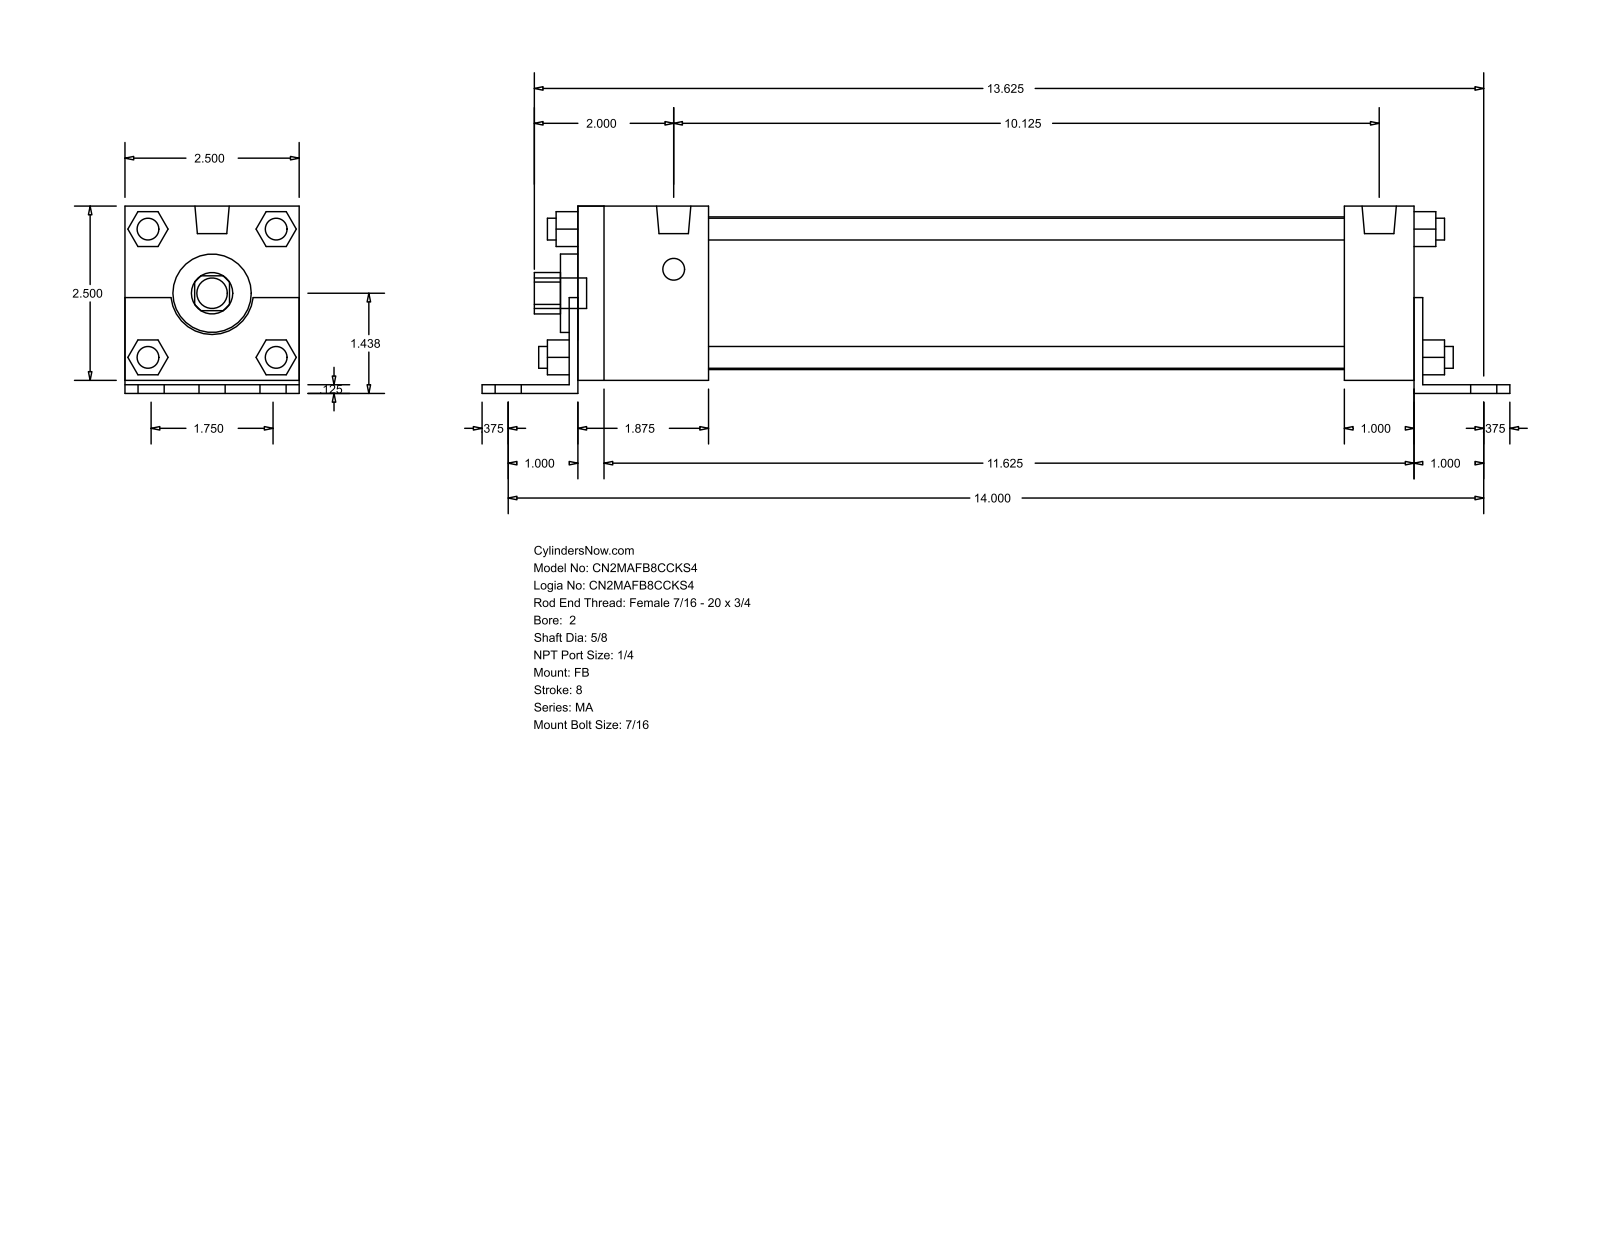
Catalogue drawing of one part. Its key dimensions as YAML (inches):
part_name: "MA_FB__0200_0.625"
step_written_by: "GSSL Pune (CONFIG_CONTROL_DESIGN)"
units: inches
bodies: {solids: 0, faces: 140, planar: 105, cylindrical: 35, other: 0}
overall_size: [14.75, 2.687, 2.5]
round_holes:
  - {diameter: 0.625, count: 1}
  - {diameter: 1.125, count: 1}
  - {diameter: 2.19, count: 1}
round_bosses_or_shafts:
  - {diameter: 0.313, count: 8}
  - {diameter: 0.437, count: 7}
  - {diameter: 0.492, count: 2}
partial_cylinders:
  - {radius: 0.297, count: 1}
  - {radius: 0.593, count: 1}
face_to_face_distances: [2.5, 0.125, 0.187, 2.687, 0.063, 2.563, 12, 12.25, 0.125, 12.125]
